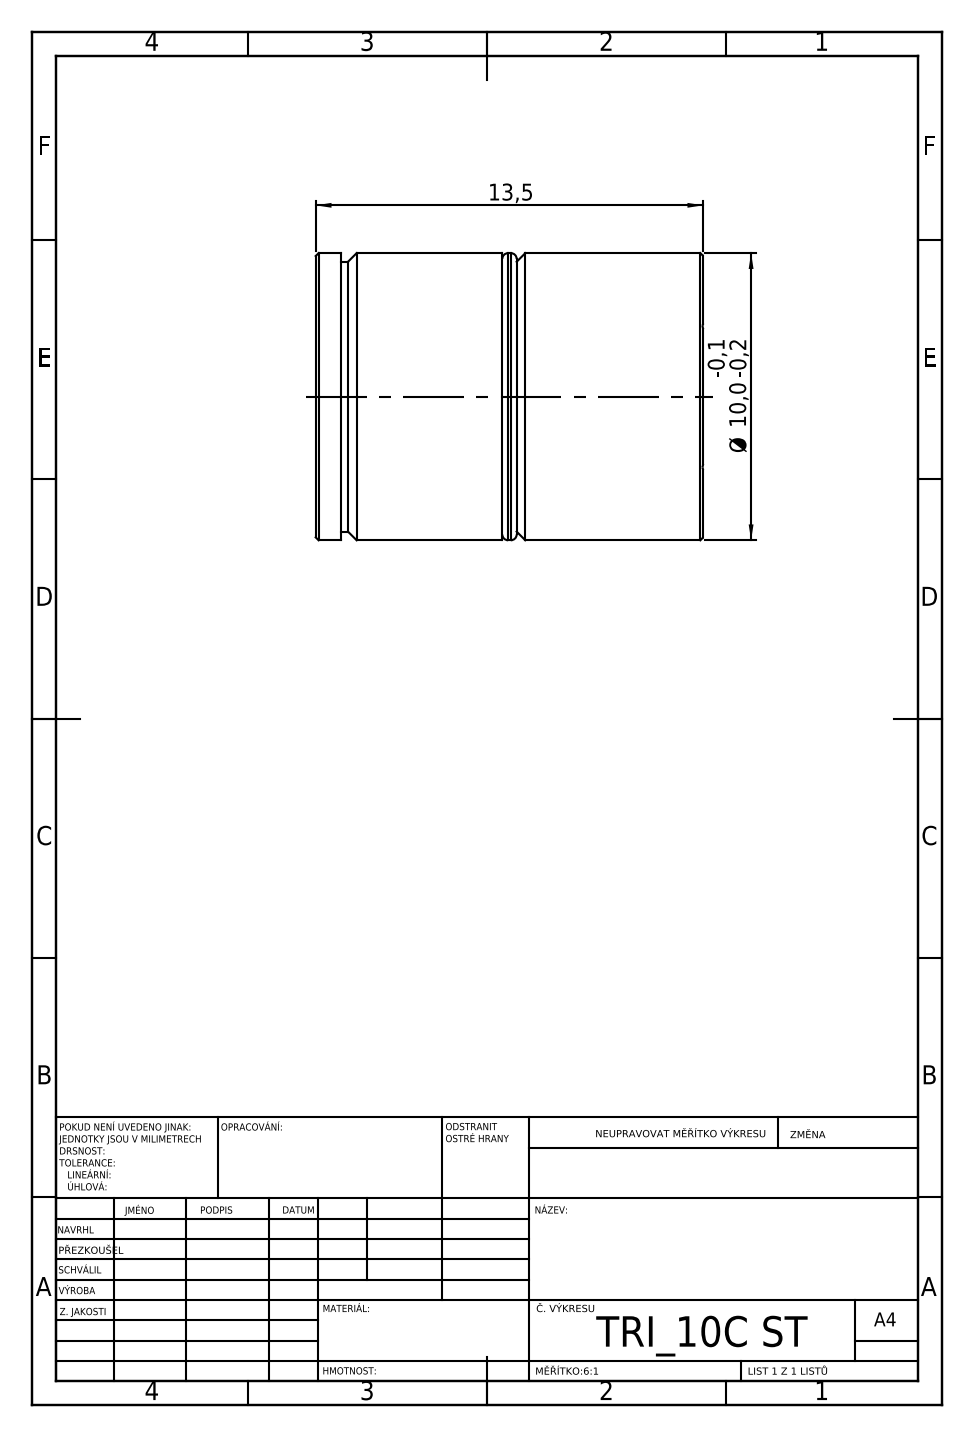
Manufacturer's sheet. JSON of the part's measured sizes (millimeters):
{"step_written_by": "SolidWorks 2019 (CONFIG_CONTROL_DESIGN)", "units": "millimeters", "bodies": {"solids": 2, "faces": 48, "planar": 24, "cylindrical": 12, "other": 12}, "overall_size": [13.5, 10, 10], "volume_mm3": 1030, "surface_area_mm2": 794, "round_bosses_or_shafts": [[10, 1], [9.4, 1]], "face_to_face_distances": [6.5, 7, 0.5, 5.5, 6, 12.5, 1, 13.5, 8.2, 12.63]}
